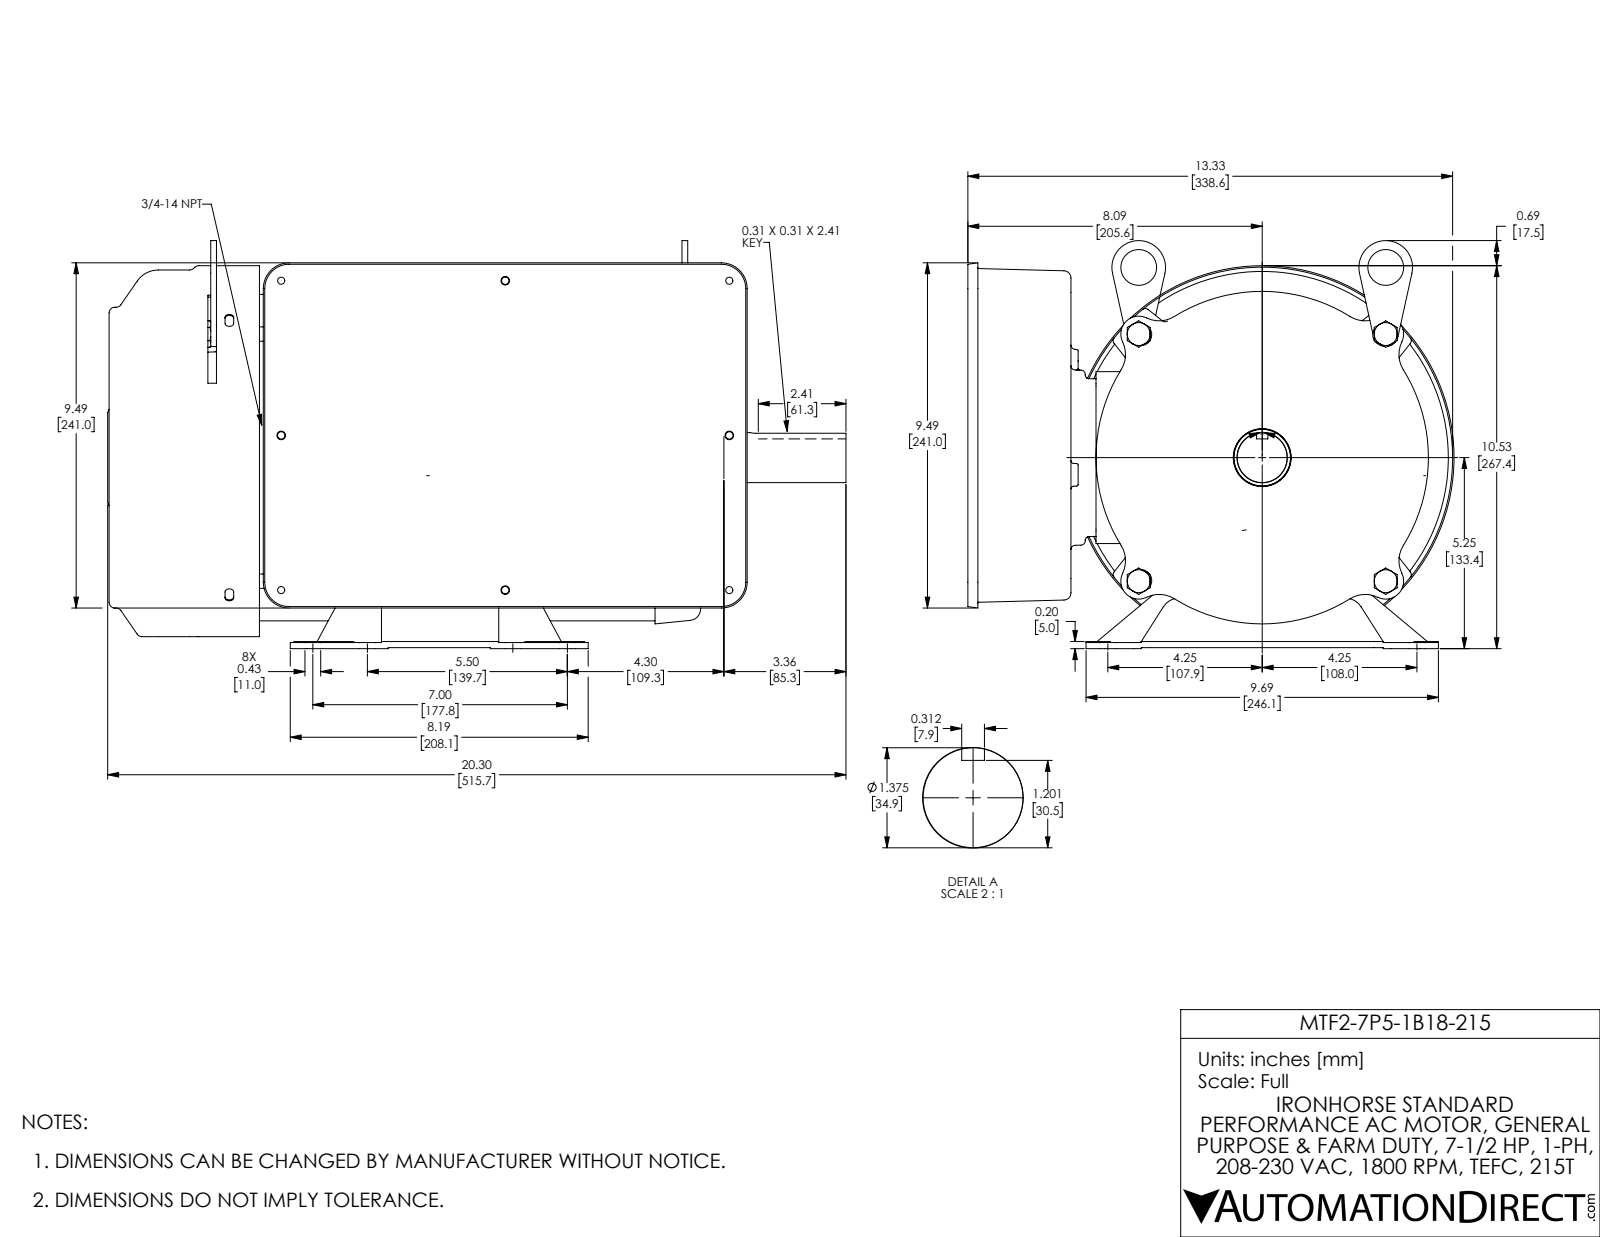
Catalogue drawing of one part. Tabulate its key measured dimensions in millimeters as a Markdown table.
| quantity | value |
| --- | --- |
| part name | MTF2-7P5-1B18-215 |
| STEP written by | SolidWorks 2017 (AUTOMOTIVE_DESIGN) |
| units | millimeters |
| bodies | 24 solids, 3480 faces (1086 planar, 847 cylindrical, 1547 other) |
| overall size | 515.7 × 339.6 × 284.9 |
| volume | 4 103 000 mm³ |
| surface area | 1 679 000 mm² |
| round holes (diameter × count) | 5.2 × 9, 6 × 9, 11 × 8, 5 × 7, 12 × 5, 11.6 × 4, 10.2 × 3, 7.1 × 2, 9 × 2, 23 × 2, 25 × 2, 8 × 1 |
| round bosses / shafts (diameter × count) | 10 × 4, 8.4 × 4, 15.4 × 3, 11.3 × 2, 268 × 1, 262 × 1, 227.9 × 1, 210 × 1 |
| partial cylindrical surfaces (radius × count) | 1 × 48, 2 × 38, 3 × 31, 5 × 30, 1.5 × 18, 0.5 × 16, 4 × 9, 15 × 8 |
| main face-to-face distances | 1, 5, 72, 71, 67, 66, 4.1, 65, 17.5, 22.5 |
| hole center spacings | 86.3, 195, 172.5, 266.8, 38.1, 80, 88.6, 108 |
